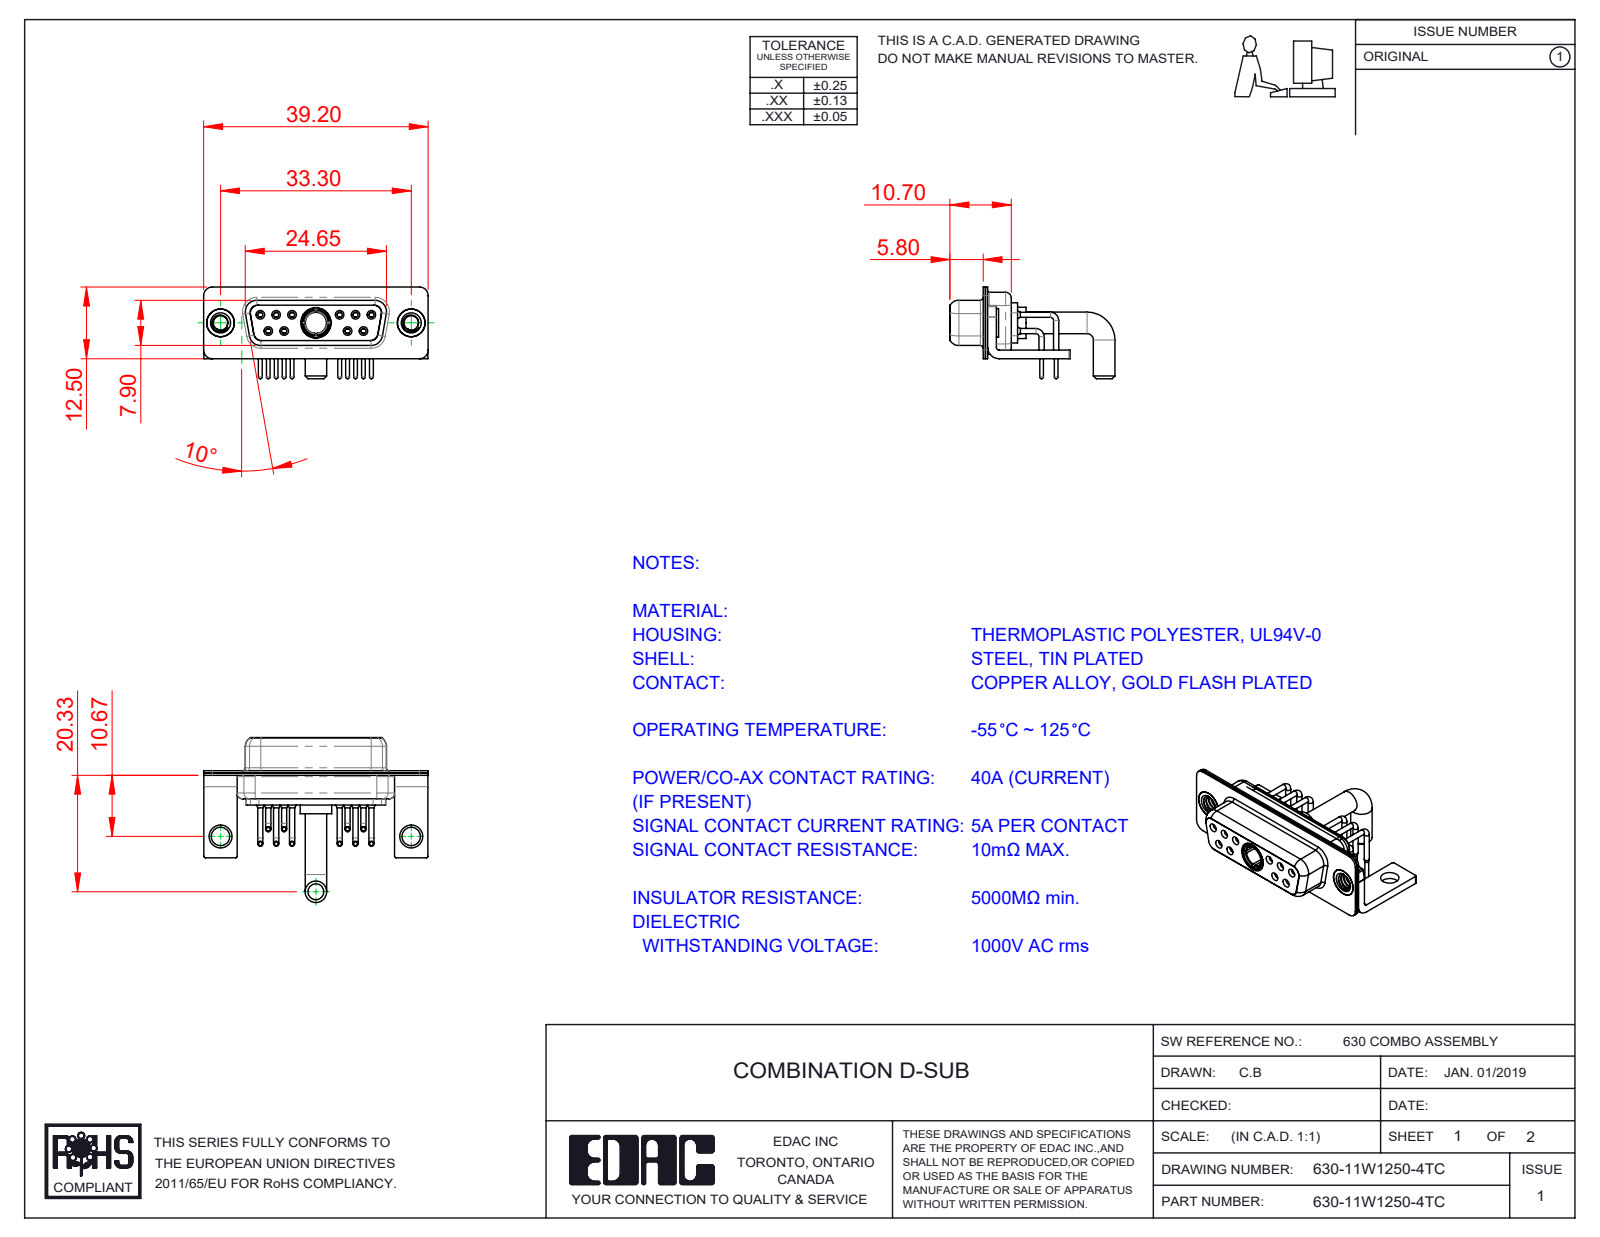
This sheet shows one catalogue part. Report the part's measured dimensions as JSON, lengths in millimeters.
{"part_name": "630Combo Contact Row 2; 630Combo Stabilizer Bracket; 630-11W1250-4TC; 630Combo Shell Rear_15 Contacts (+5 more)", "step_written_by": "SolidWorks 2020 (CONFIG_CONTROL_DESIGN)", "units": "millimeters", "bodies": {"solids": 19, "faces": 925, "planar": 266, "cylindrical": 410, "other": 249}, "overall_size": [39.2, 28.8, 16], "volume_mm3": 3059, "surface_area_mm2": 6988, "round_holes": [[0.9, 10], [1.1, 10], [1.5, 10], [2, 10], [1.7, 6], [1.6, 4], [4.85, 3], [2.5, 2], [3.2, 2], [4, 2], [4.05, 2], [3.7, 1]], "round_bosses_or_shafts": [[0.9, 10], [0.65, 10], [1.6, 6], [5, 2], [4.95, 2], [4.8, 2], [3.75, 2], [5.5, 1]], "partial_cylinders_radius": [[0.25, 16], [1.5, 16], [2, 13], [1.35, 12], [1.6, 8], [0.5, 5], [0.6, 4], [0.65, 4]], "face_to_face_distances": [0.4, 0.8, 1.4, 0.45, 8.45, 1.5, 1.8, 8.9, 6.2, 2.3], "hole_center_spacings": [3.16, 2.77, 13.85, 11.08, 16.62, 5.03, 5.04, 5.54]}
